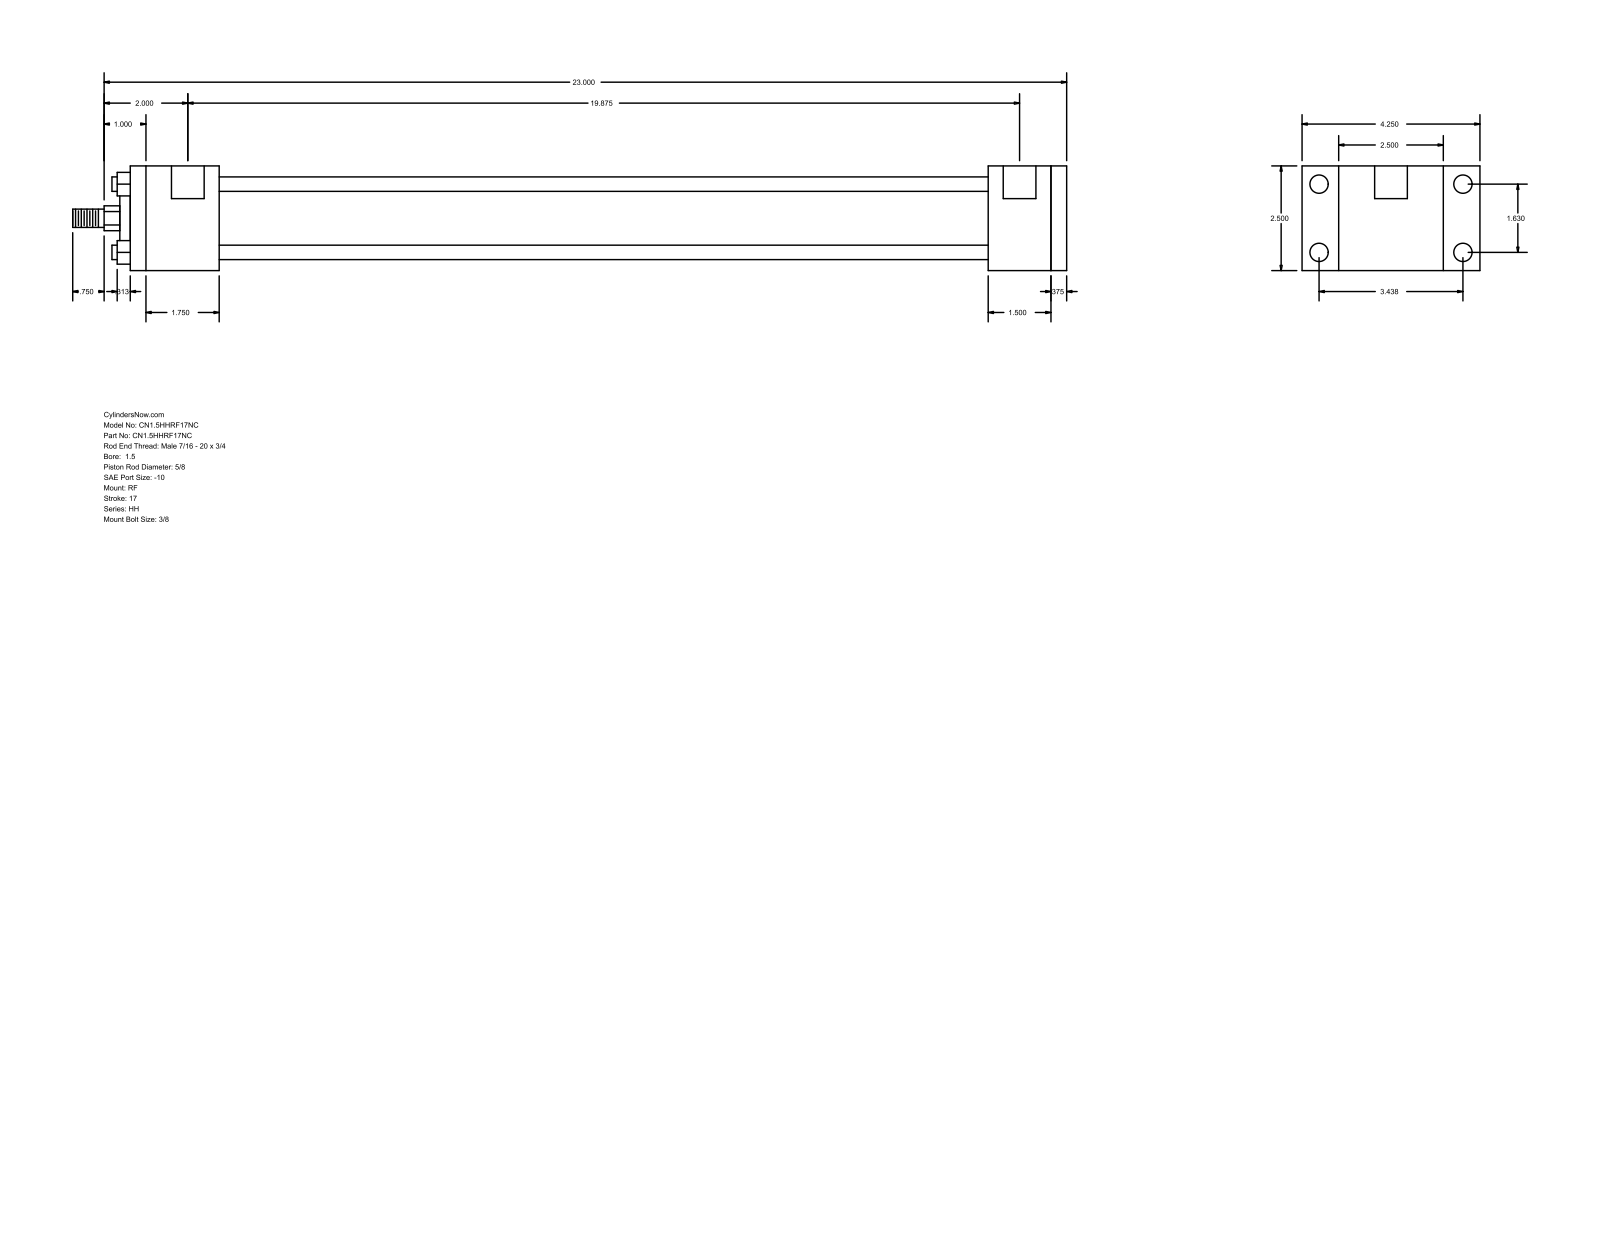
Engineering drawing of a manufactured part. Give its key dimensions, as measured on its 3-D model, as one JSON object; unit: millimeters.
{"part_name": "HH_RF__0150_0.625", "step_written_by": "GSSL Pune (CONFIG_CONTROL_DESIGN)", "units": "millimeters", "bodies": {"solids": 0, "faces": 92, "planar": 64, "cylindrical": 28, "other": 0}, "overall_size": [603.25, 107.95, 63.5], "round_holes": [[5.56, 4], [11.13, 4], [19.84, 2]], "round_bosses_or_shafts": [[8.76, 4], [44.45, 1], [28.57, 1], [15.88, 1], [11.11, 1]], "partial_cylinders_radius": [[7.54, 1]], "face_to_face_distances": [63.5, 568.32, 9.53, 558.79, 53.97, 520.7, 466.73, 504.82, 514.35, 38.09], "hole_center_spacings": [1.59, 41.4, 87.32, 96.64, 506.41, 508, 504.82]}
